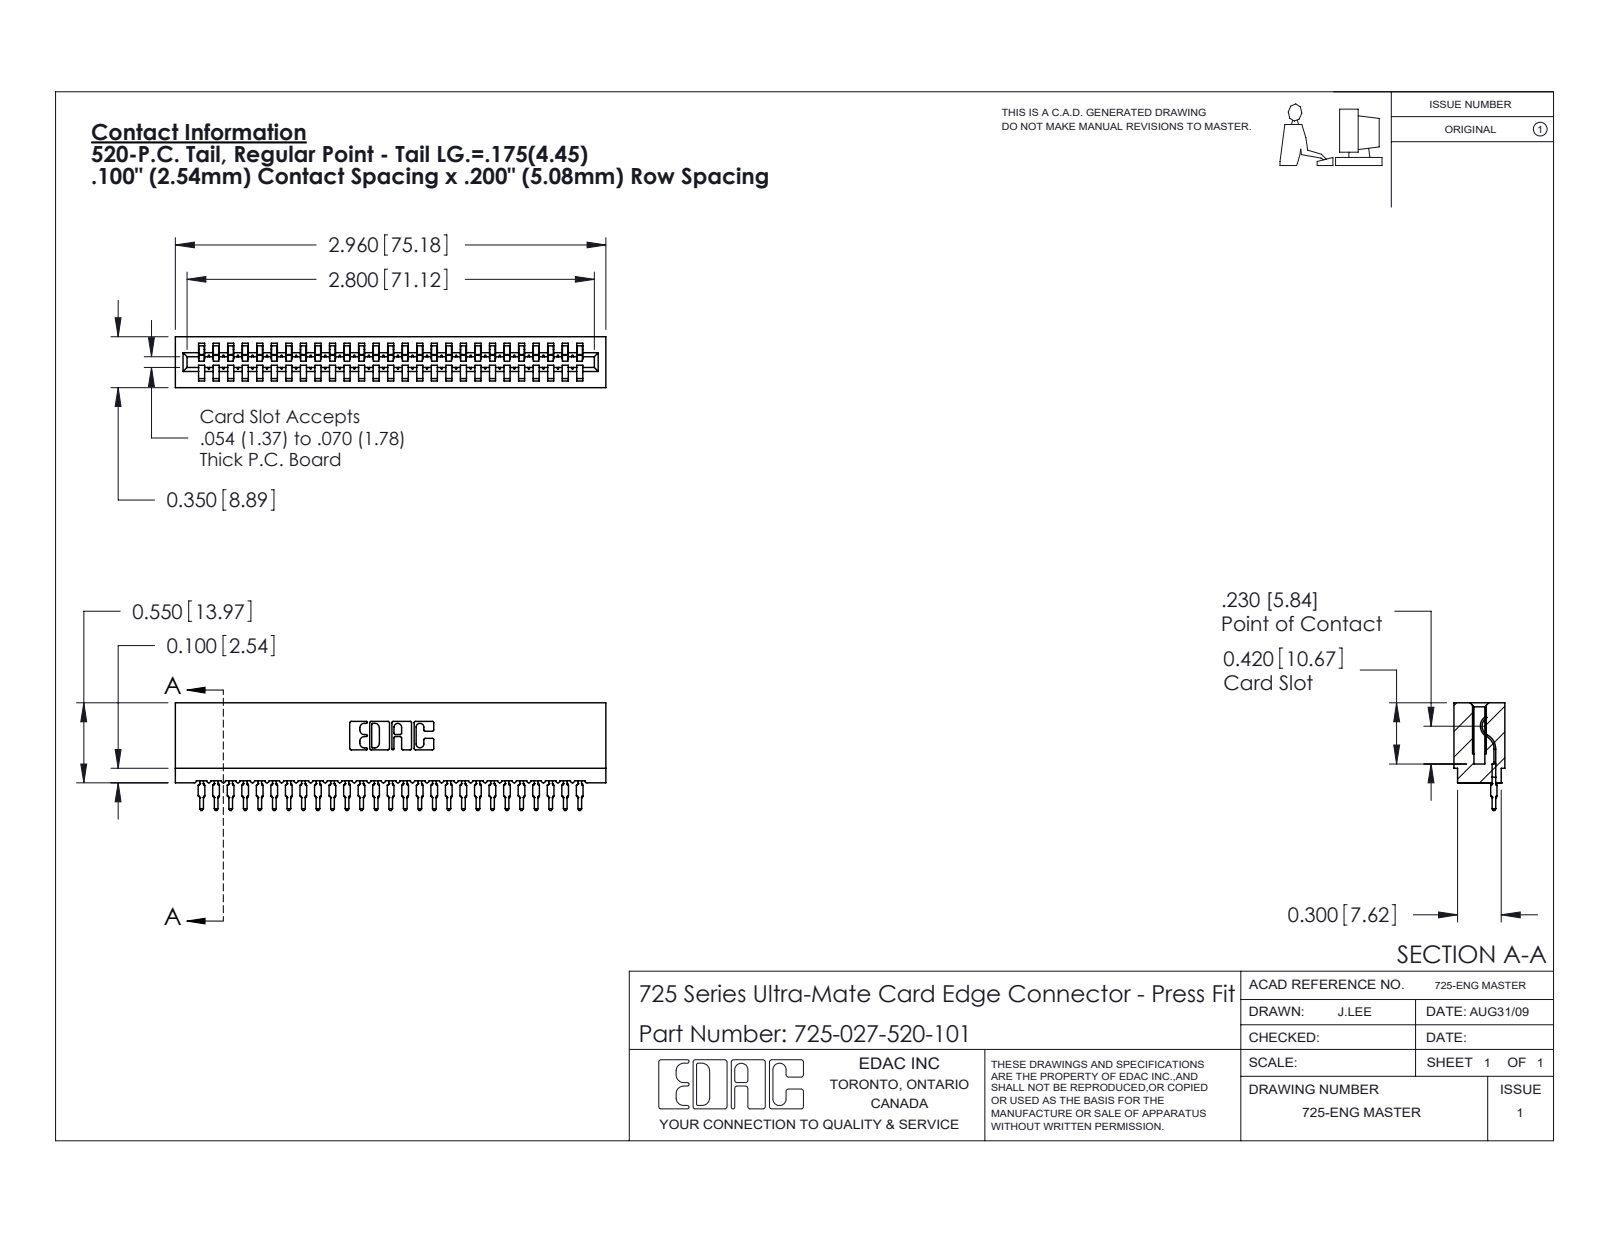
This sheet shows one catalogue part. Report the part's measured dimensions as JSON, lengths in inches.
{"part_name": "725 Part_Insulator Option - 01; 725-027-520-101; 745-292-001_520", "step_written_by": "SolidWorks 2020 (CONFIG_CONTROL_DESIGN)", "units": "inches", "bodies": {"solids": 28, "faces": 3119, "planar": 1864, "cylindrical": 553, "other": 702}, "overall_size": [2.96, 0.741, 0.35], "volume_in3": 0.351, "surface_area_in2": 16.5, "partial_cylinders_radius": [[0.015, 54], [0.021, 54], [0.01, 22], [0.007, 6], [0.031, 6], [0.005, 4], [0.011, 4], [0.026, 3]], "face_to_face_distances": [0.1, 0.35, 0.2, 0.6, 0.3, 0.212, 0.138, 0.4, 0.7, 0.045]}
